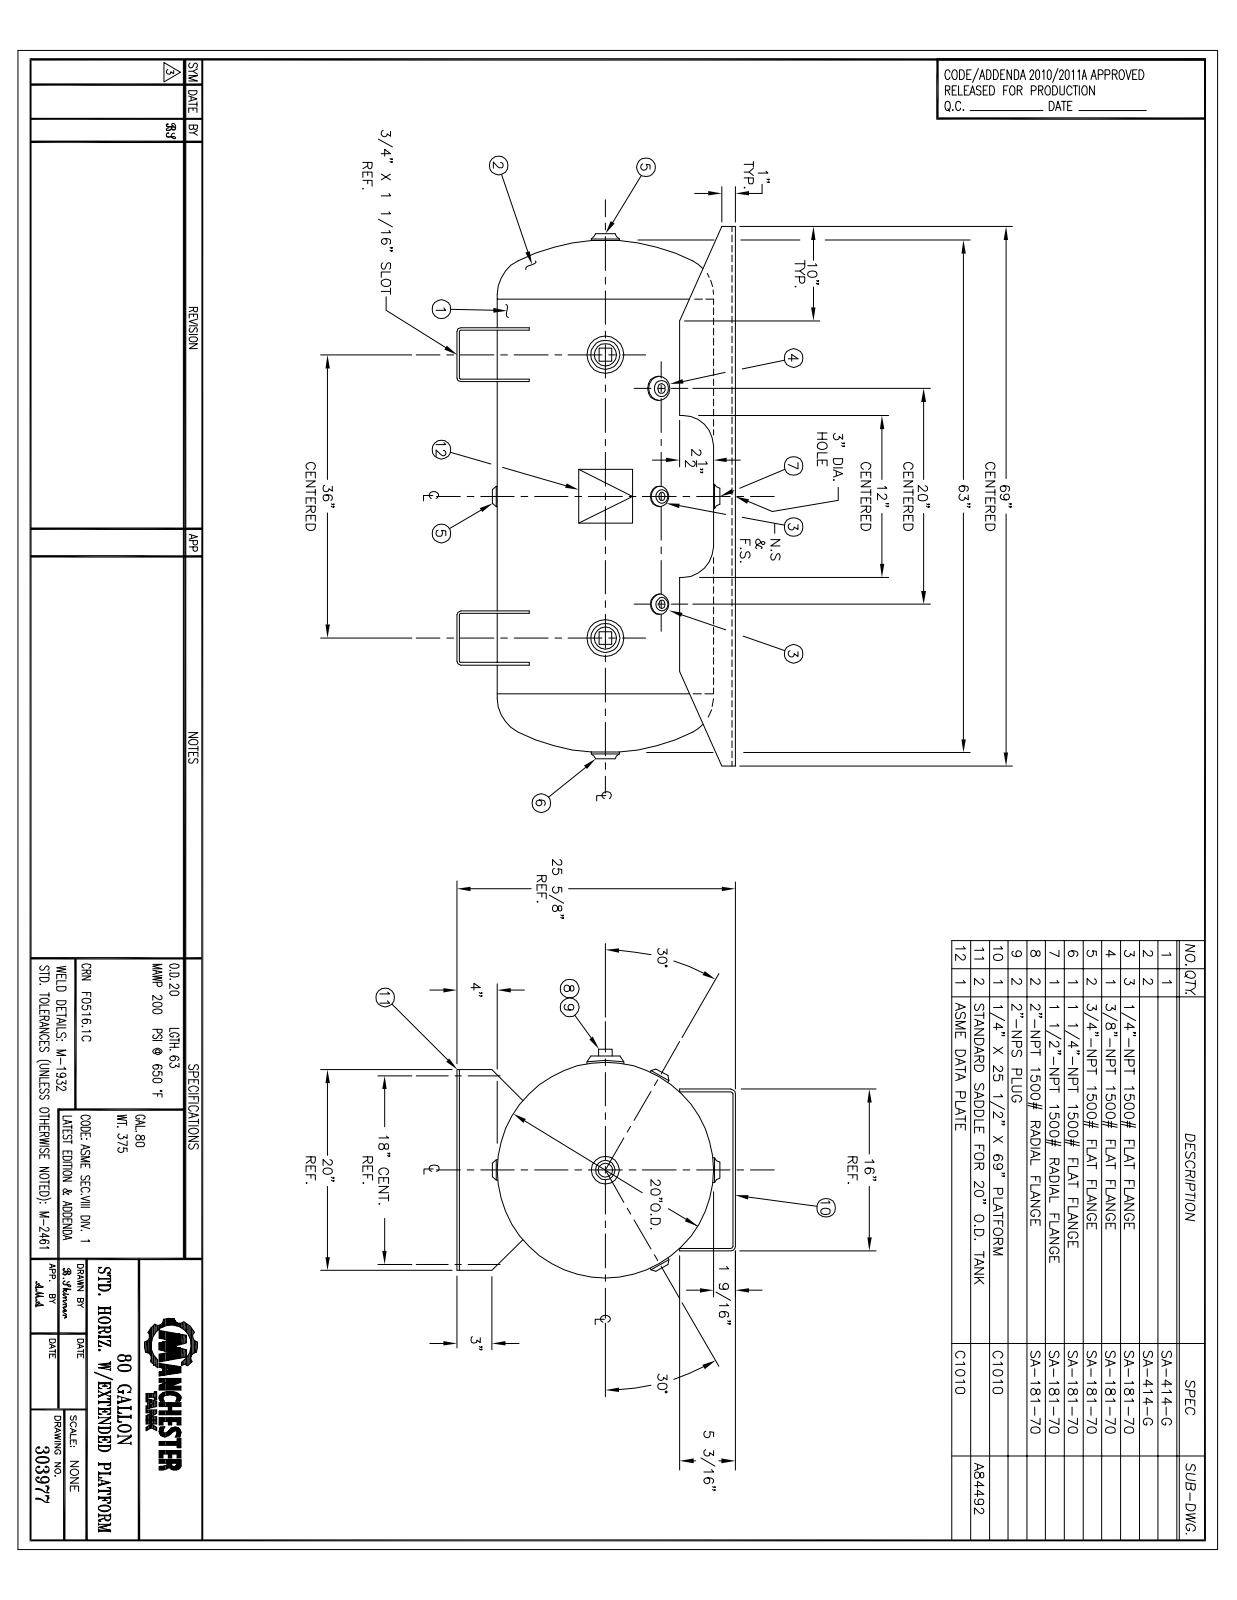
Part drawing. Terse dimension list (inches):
name: 303977
written by: SolidWorks 2012 (CONFIG_CONTROL_DESIGN)
unit: in
bodies: 0 solids, 277 faces (118 planar, 81 cylindrical, 78 other)
size: 69 × 25.475 × 21.531
holes: 3× ⌀0.54, 2× ⌀1.05, 1× ⌀0.675, 1× ⌀1, 1× ⌀1.063, 1× ⌀1.66, 1× ⌀1.9, 1× ⌀3, 1× ⌀19.698
bosses: 3× ⌀2.375, 3× ⌀1.5, 2× ⌀3, 2× ⌀1.63, 2× ⌀1.625, 1× ⌀20, 1× ⌀2.38, 1× ⌀1.625
rounds: 8× R0.375, 4× R0.094, 4× R0.281, 2× R0.25, 2× R0.474, 2× R2.5, 1× R10.06
face distances: 0.224, 0.187, 15.776, 36, 5.813, 15.552, 16, 25.251, 25.475, 25.064
hole spacings: 10, 20
